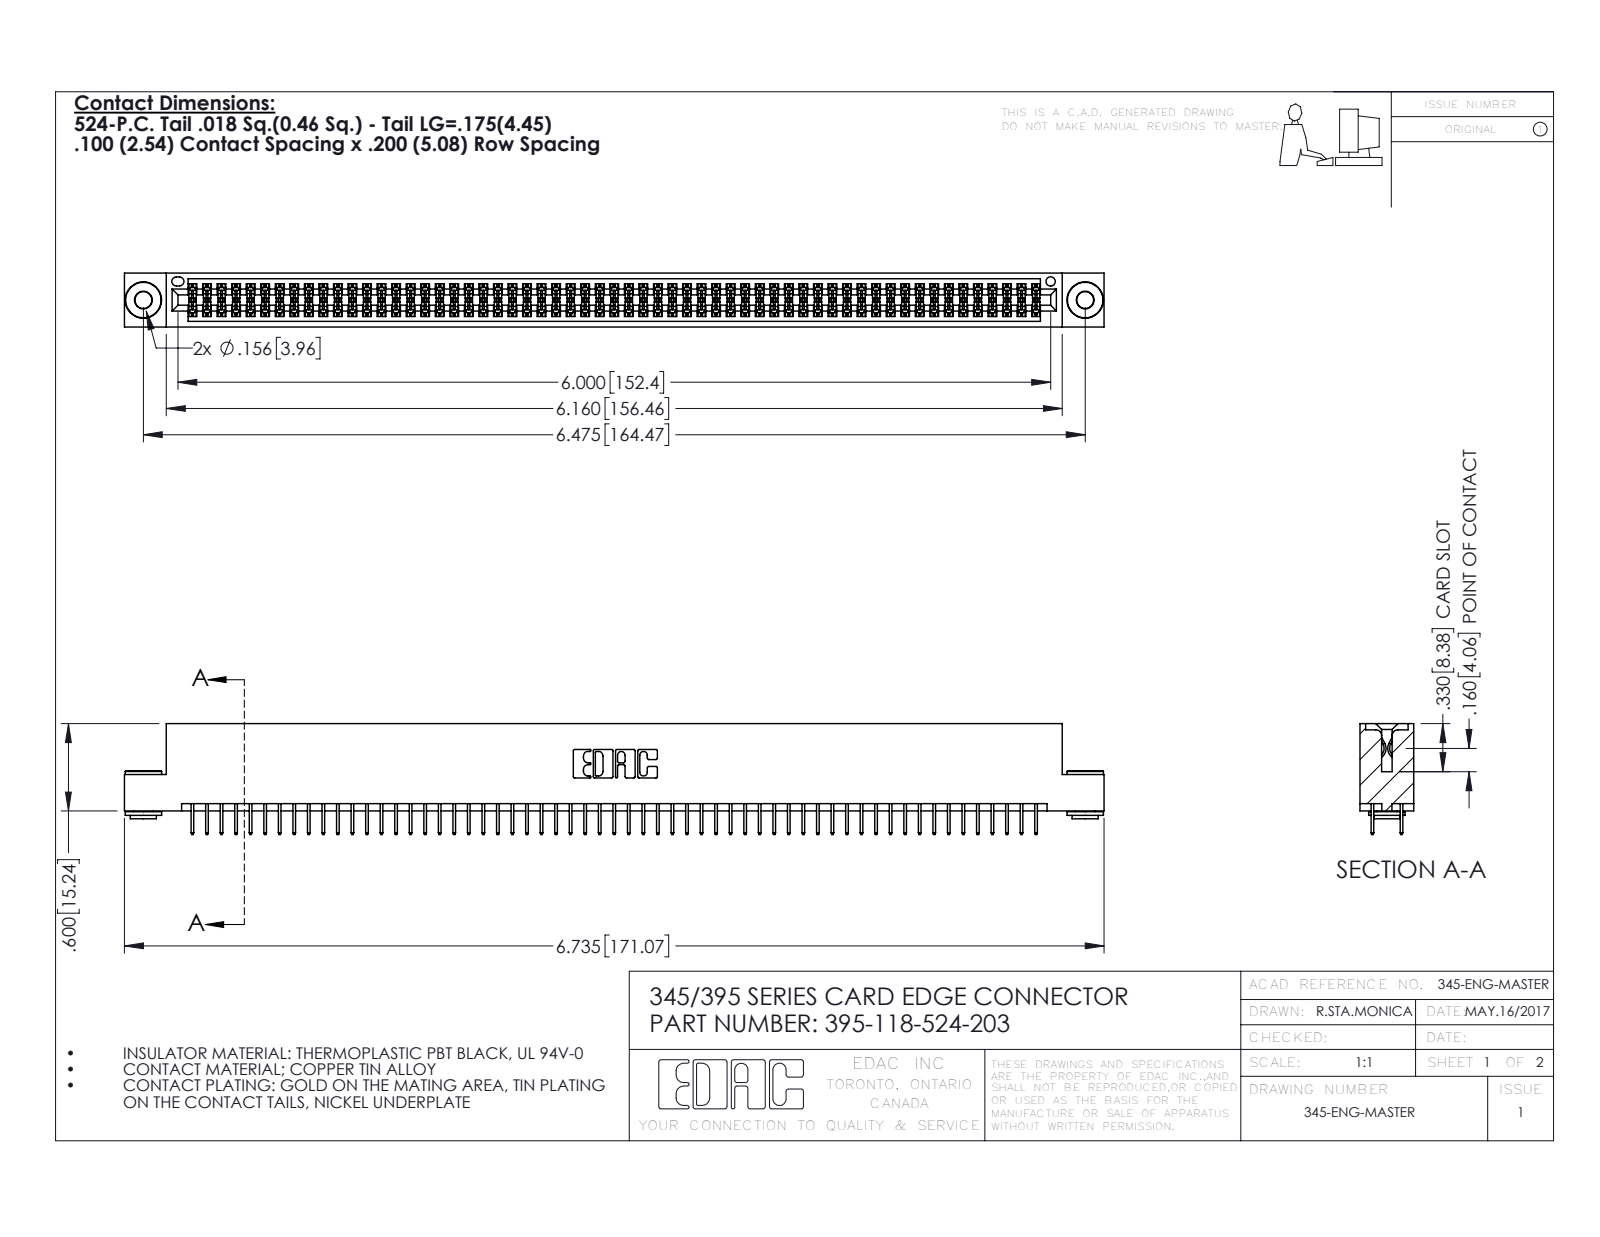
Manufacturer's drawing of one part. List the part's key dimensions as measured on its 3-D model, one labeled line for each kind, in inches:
Part name (STEP PRODUCT): 395-118-524-203; 345 Part_Flush Mounting Lugs - 0.156 Dia-TH; 345-250-002_345-250-002-102; 345-292-001_345-293-124
STEP written by: SolidWorks 2016 (CONFIG_CONTROL_DESIGN)
Units: inches
Bodies: 121 solids, 6536 faces (4692 planar, 1836 cylindrical, 8 other)
Overall size (bounding box): 6.735 × 0.762 × 0.37
Volume: 1.014 in³ · Surface area: 38.17 in²
Round holes (diameter × count): ⌀0.116 ×2, ⌀0.156 ×2, ⌀0.064 ×1
Round bosses / shafts (diameter × count): ⌀0.25 ×2, ⌀0.18 ×2, ⌀0.136 ×2
Partial cylindrical surfaces — rounded edges, fillets, slot ends (radius × count): R0.006 ×177, R0.01 ×22, R0.007 ×6, R0.031 ×6, R0.026 ×3, R0.014 ×2, R0.019 ×2, R0.022 ×2
Main face-to-face distances: 0.072, 0.298, 0.2, 0.37, 0.025, 0.098, 0.272, 0.225, 0.072, 0.175
Hole centre spacings: 0.27, 6.239, 6.475
